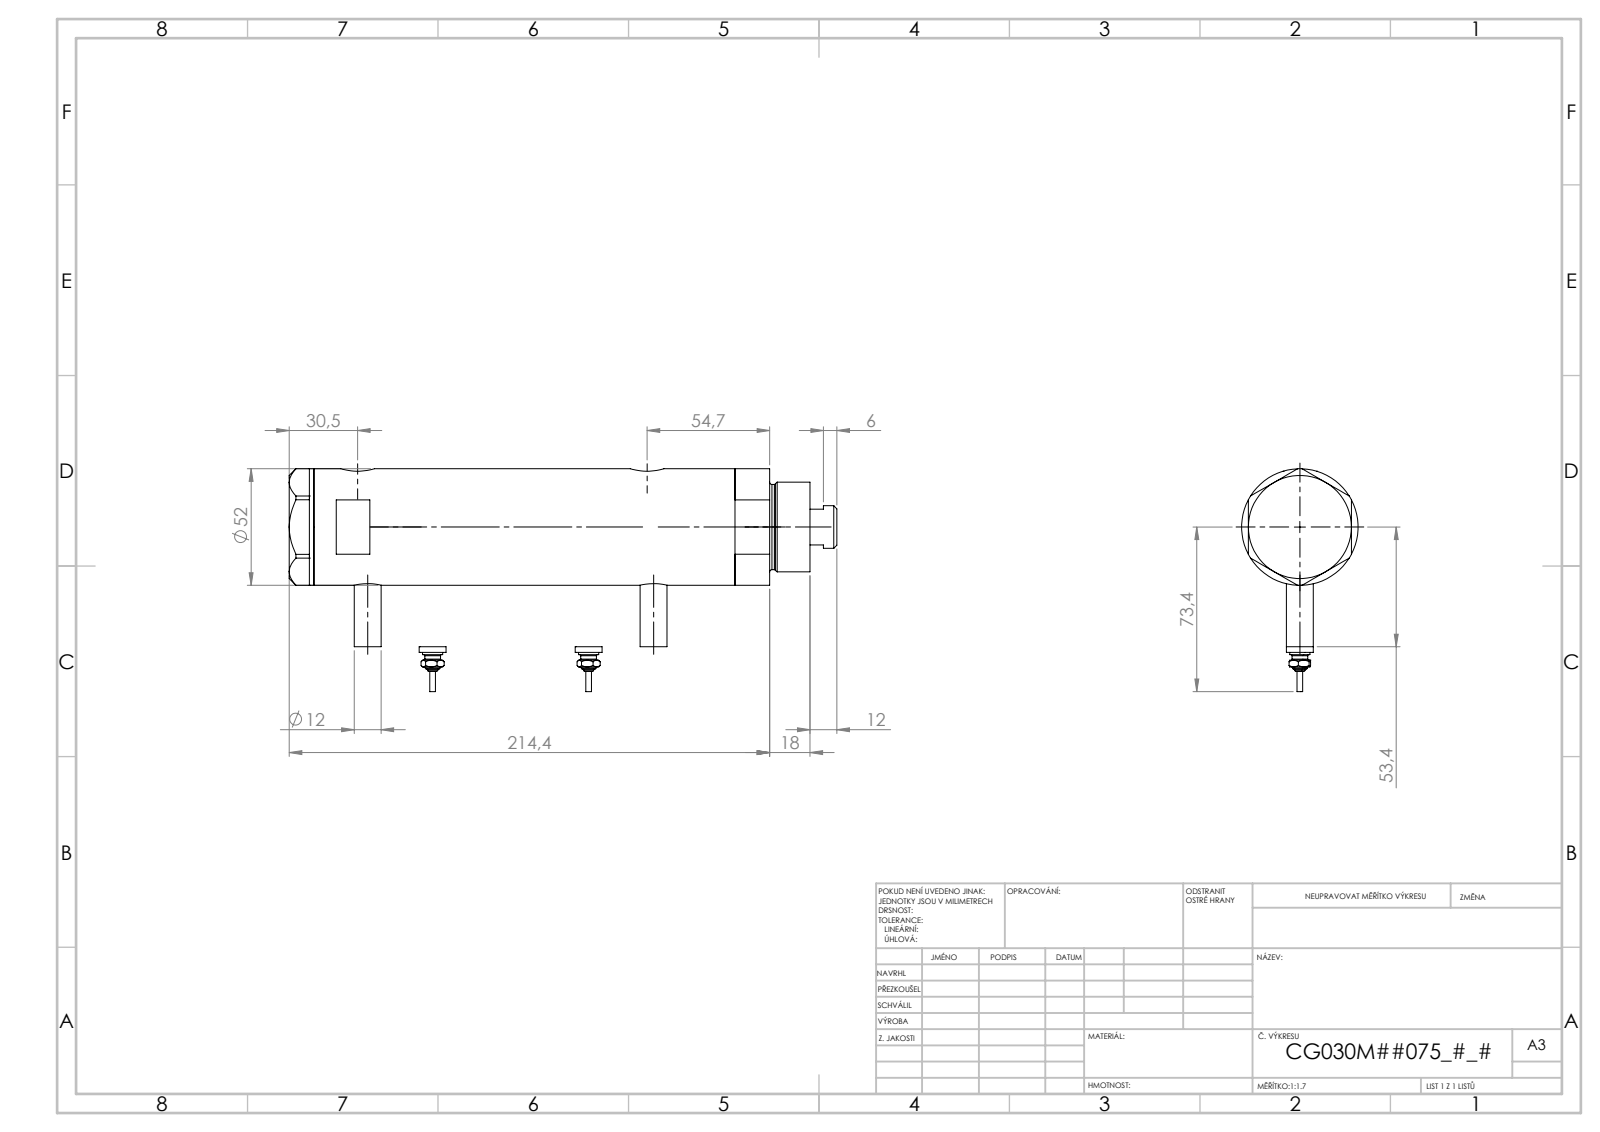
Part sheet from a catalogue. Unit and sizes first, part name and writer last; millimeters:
Units: millimetres
Overall size (bounding box): 224.02 × 84.3 × 52
Round holes (diameter × count): ⌀5 ×2, ⌀9.73 ×2, ⌀12.5 ×2, ⌀15 ×2, ⌀6.5 ×1, ⌀20 ×1, ⌀21.5 ×1, ⌀30 ×1, ⌀33 ×1, ⌀44 ×1
Round bosses / shafts (diameter × count): ⌀12 ×3, ⌀9 ×2, ⌀7 ×2, ⌀4.34 ×2, ⌀2.4 ×2, ⌀52 ×1, ⌀40 ×1, ⌀38 ×1
Main face-to-face distances: 128.54, 23.8, 104.74, 11, 34.8, 139.54, 46, 175.94, 164.94, 141.14
Hole centre spacings: 2.9, 4.5, 101.75, 104.65, 106.25, 109.15, 2.89, 2.91
Volume: 400 201 mm³ · Surface area: 91 069 mm²
Bodies: 6 solids, 246 faces (95 planar, 77 cylindrical, 74 other)
Part name (STEP PRODUCT): V270CG_SWITCH; V270CG_VC; V270CG_MIDDLE; V270CG_BACK (+1 more)
STEP written by: SolidWorks 2019 (CONFIG_CONTROL_DESIGN)
